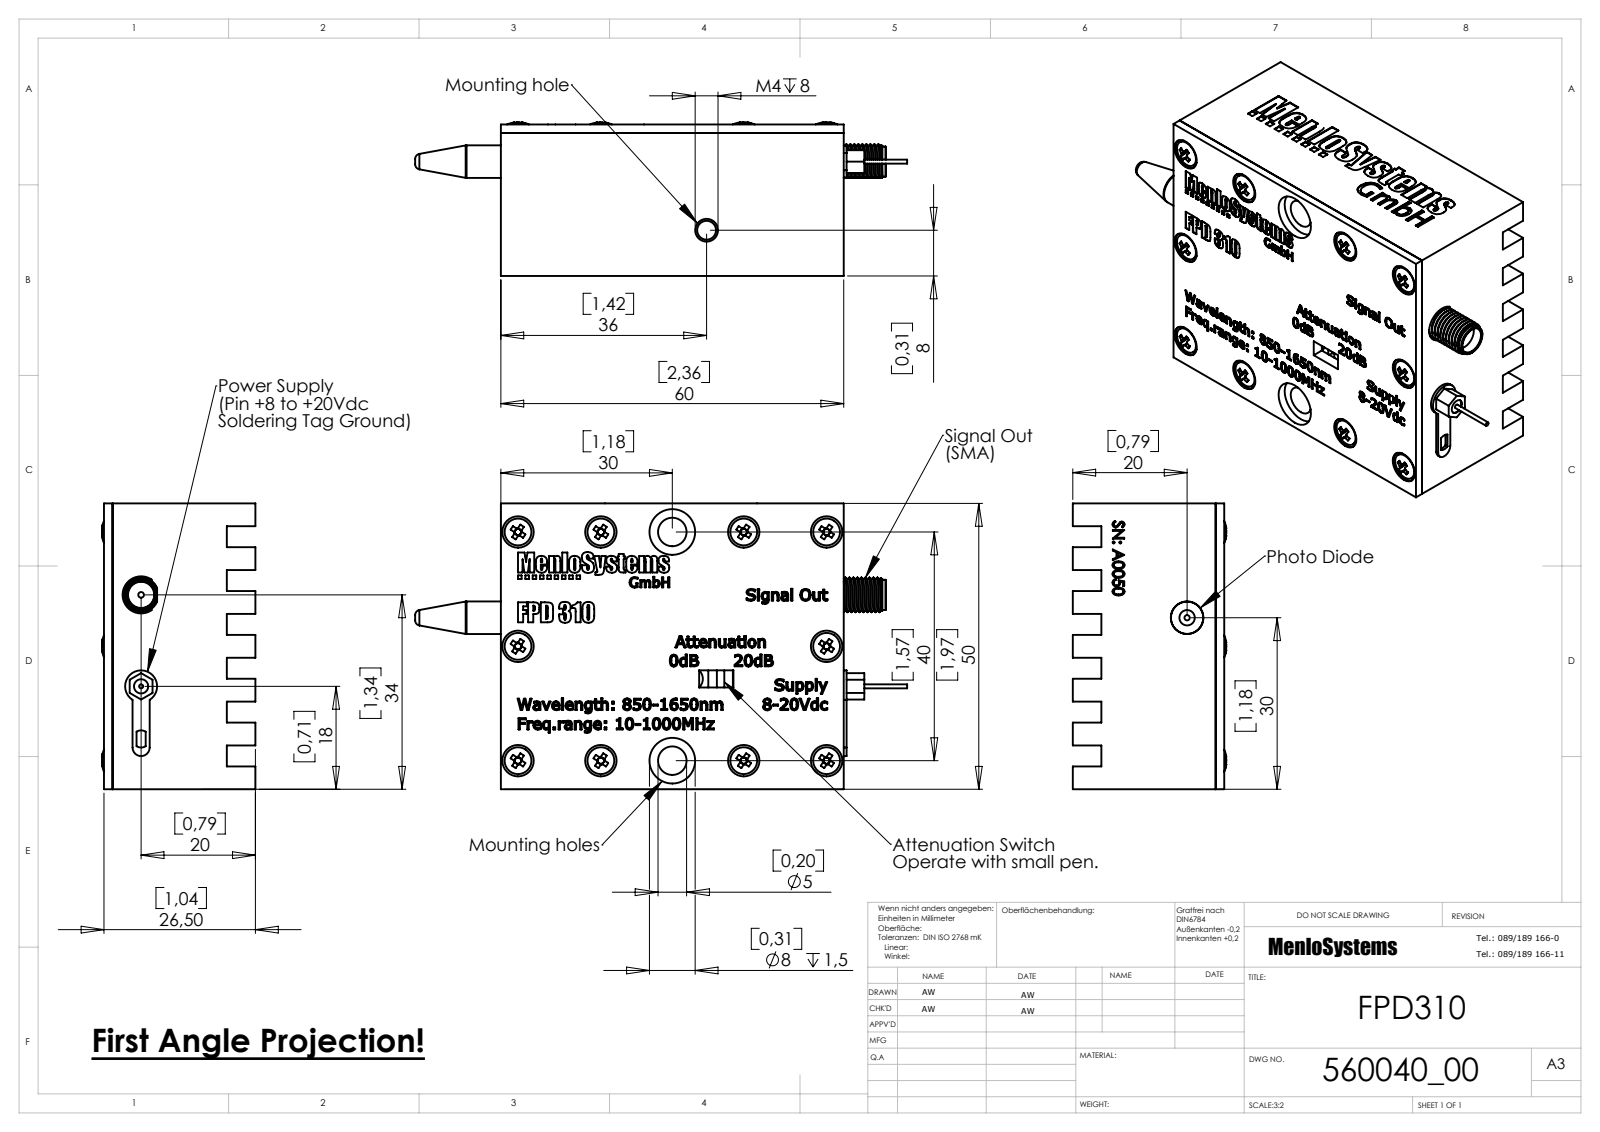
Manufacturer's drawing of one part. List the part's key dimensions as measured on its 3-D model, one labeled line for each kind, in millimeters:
Part name (STEP PRODUCT): 600238_FPD310; 600470_1_FPD310-0; SW3dPS-sma bulkhead straight jack_echt; Countersunk Raised Head Cross Recess Screw_DIN_ISO 7047 - M2.5 x 6 - Z --- 6N (+4 more)
STEP written by: SolidWorks 2007 (AUTOMOTIVE_DESIGN)
Units: millimetres
Bodies: 17 solids, 2806 faces (1499 planar, 165 cylindrical, 1142 other)
Overall size (bounding box): 86.1 × 50 × 26.85
Volume: 57 737 mm³ · Surface area: 26 996 mm²
Round holes (diameter × count): ⌀2.5 ×11, ⌀2.05 ×10, ⌀5.5 ×10, ⌀5 ×2, ⌀8 ×2, ⌀1 ×1, ⌀3 ×1, ⌀3.3 ×1, ⌀4 ×1, ⌀4.6 ×1, ⌀5.7 ×1
Round bosses / shafts (diameter × count): ⌀4.7 ×10, ⌀0.5 ×3, ⌀6.1 ×1, ⌀5.6 ×1, ⌀5.28 ×1, ⌀0.7 ×1
Partial cylindrical surfaces — rounded edges, fillets, slot ends (radius × count): R1 ×9, R2 ×4, R1.5 ×2, R2.03 ×2, R3.25 ×1
Main face-to-face distances: 10, 7.67, 1.5, 15.34, 2, 3.67, 23.01, 5, 4, 25
Hole centre spacings: 40, 12.5, 14.5, 20, 24.7, 27, 33.6, 39.5
